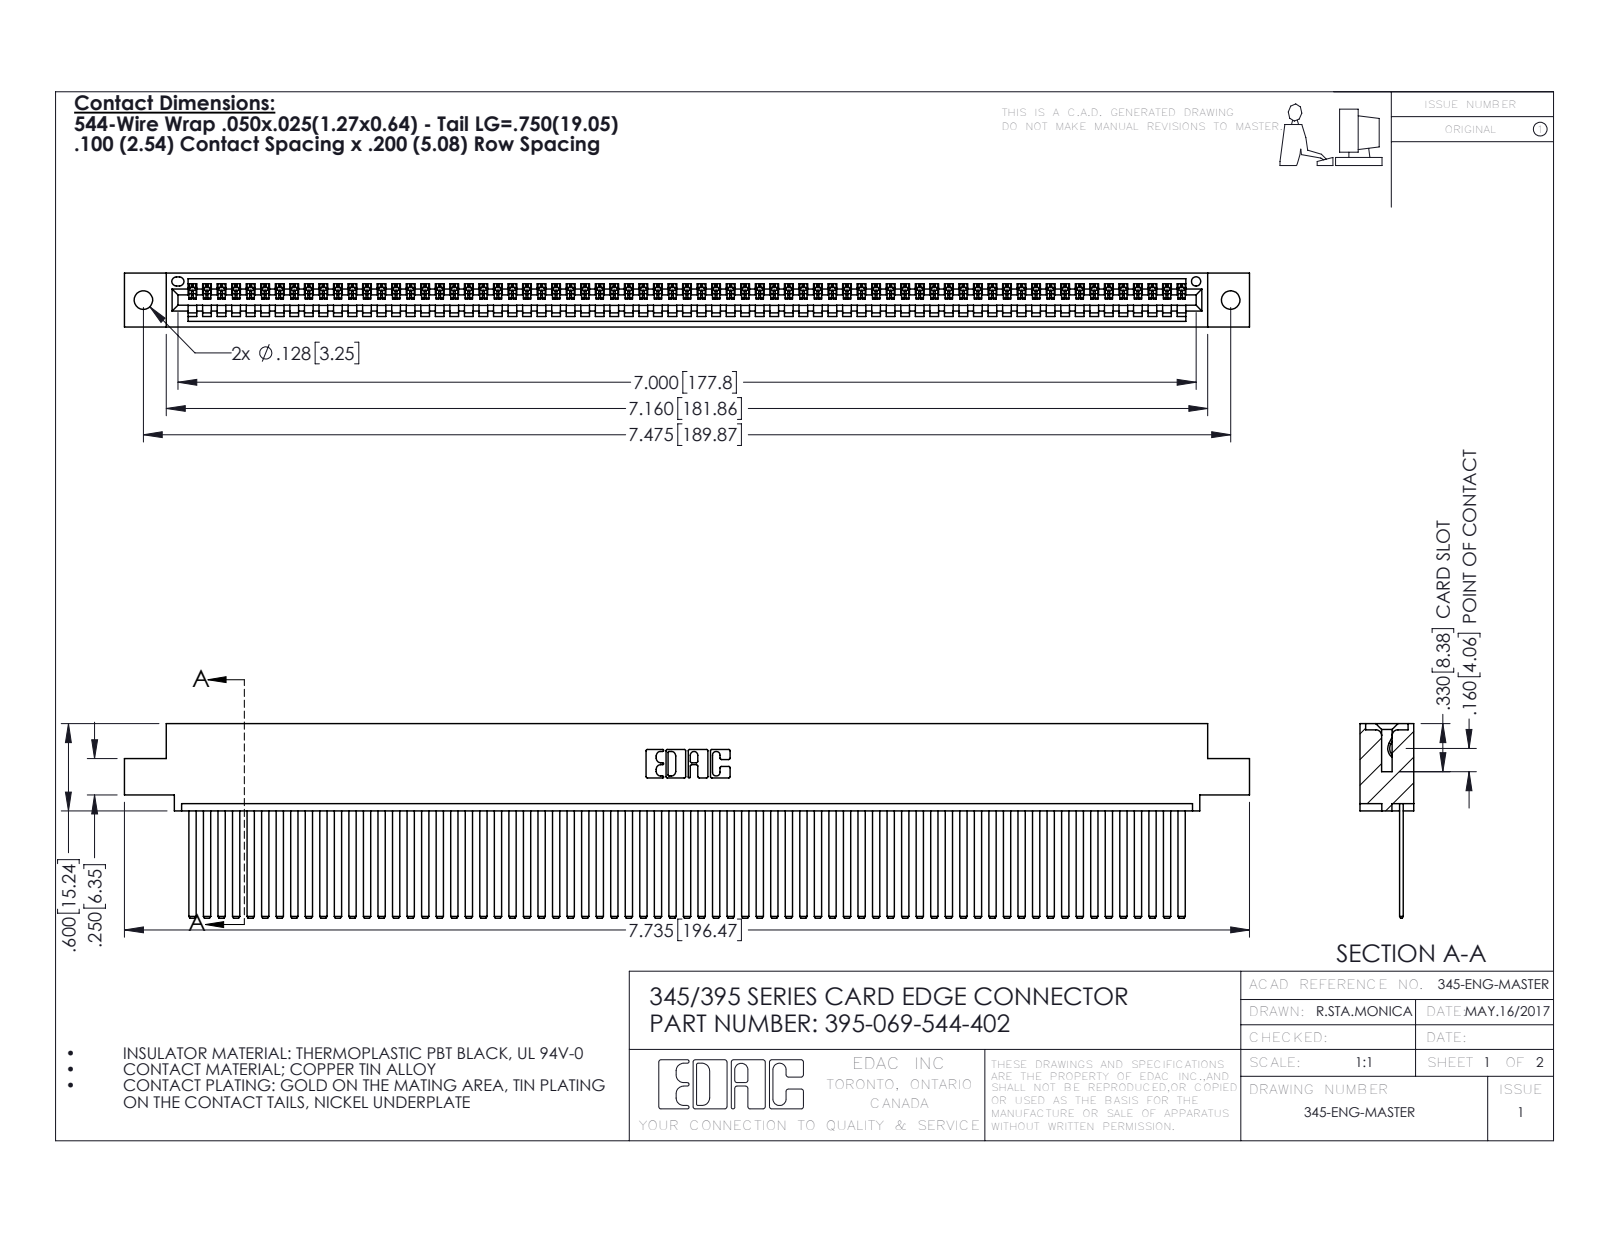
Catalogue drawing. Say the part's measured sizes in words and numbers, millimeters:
The part is named "345 Part_0.110 Offset - 0.128 Dia; 395-069-544-402; 345-292-001_345-293-144". Its 3-D file was written by "SolidWorks 2016 (CONFIG_CONTROL_DESIGN)". It is 70 solids with 3718 faces: 2568 planar, 1150 cylindrical and 0 other. Overall it measures 196.5 by 34 by 9.4 millimeters. Its volume is 19 570 cubic millimeters and its surface area 28 590 square millimeters. Round holes: 2 of diameter 3.3, 1 of diameter 1.6. Partial cylindrical surfaces (rounded edges, fillets, slot ends): 138 of radius 0.2, 22 of radius 0.3, 6 of radius 0.2, 6 of radius 0.8, 3 of radius 0.7, 2 of radius 0.8, 2 of radius 1, 1 of radius 0.4. The main face-to-face distances are 1.8, 7.6, 0.6, 2.5, 6.9, 9.4, 5.1, 5.7, 3.8, 1.8. The hole center spacings are 6.9, 183.9, 189.9.
